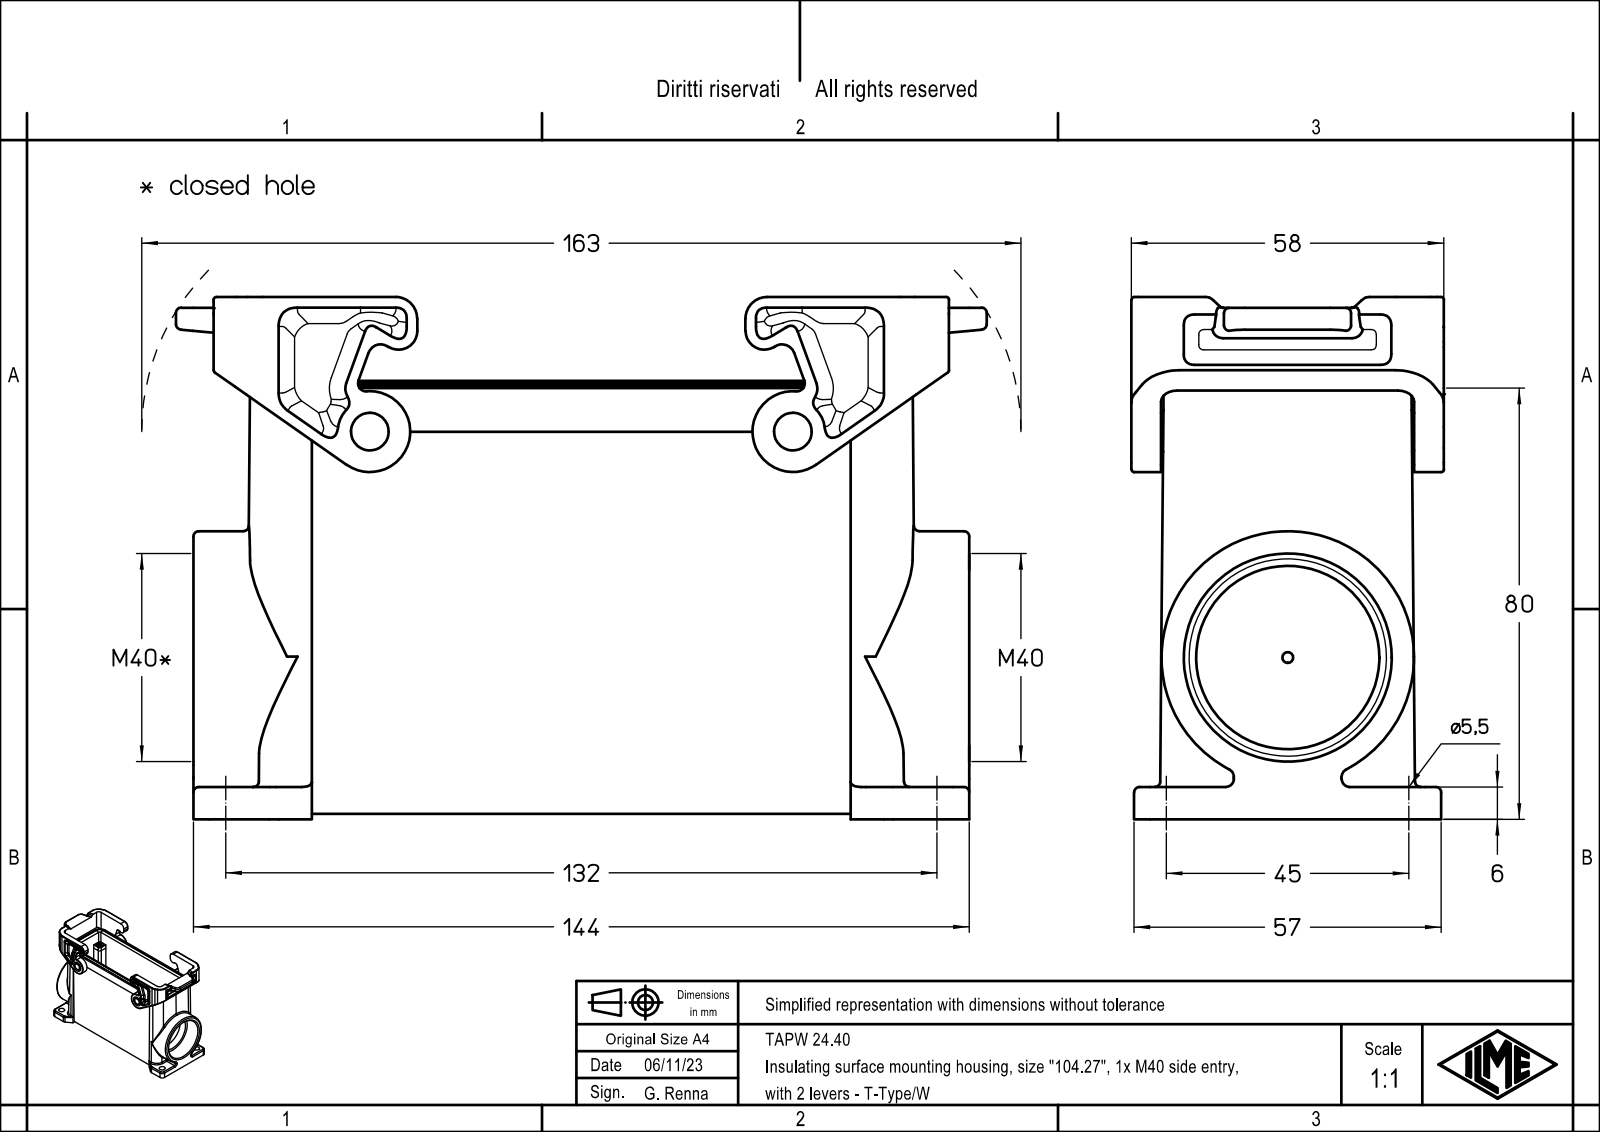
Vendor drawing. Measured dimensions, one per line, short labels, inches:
name: TAPW 24.40
written by: Creo Elements/Direct Modeling 20.1B 02-Apr-2019 (C) Parametric Technology GmbH (AUTOMOTIVE_DESIGN)
unit: in
bodies: 1 solid, 414 faces (204 planar, 158 cylindrical, 52 other)
size: 5.925 × 3.815 × 2.283
volume: 12.84 in³; area: 125.5 in²
holes: 4× ⌀0.217, 1× ⌀1.339, 1× ⌀1.52
bosses: 2× ⌀0.276, 1× ⌀1.845
rounds: 20× R0.118, 16× R0.039, 16× R0.079, 10× R0.059, 8× R0.051, 8× R0.236, 8× R0.276, 6× R0.157
face distances: 1.386, 0.217, 0.232, 1.618, 0.039, 0.256, 0.449, 1.835, 2.067, 0.197
hole spacings: 1.772, 5.197, 5.491
